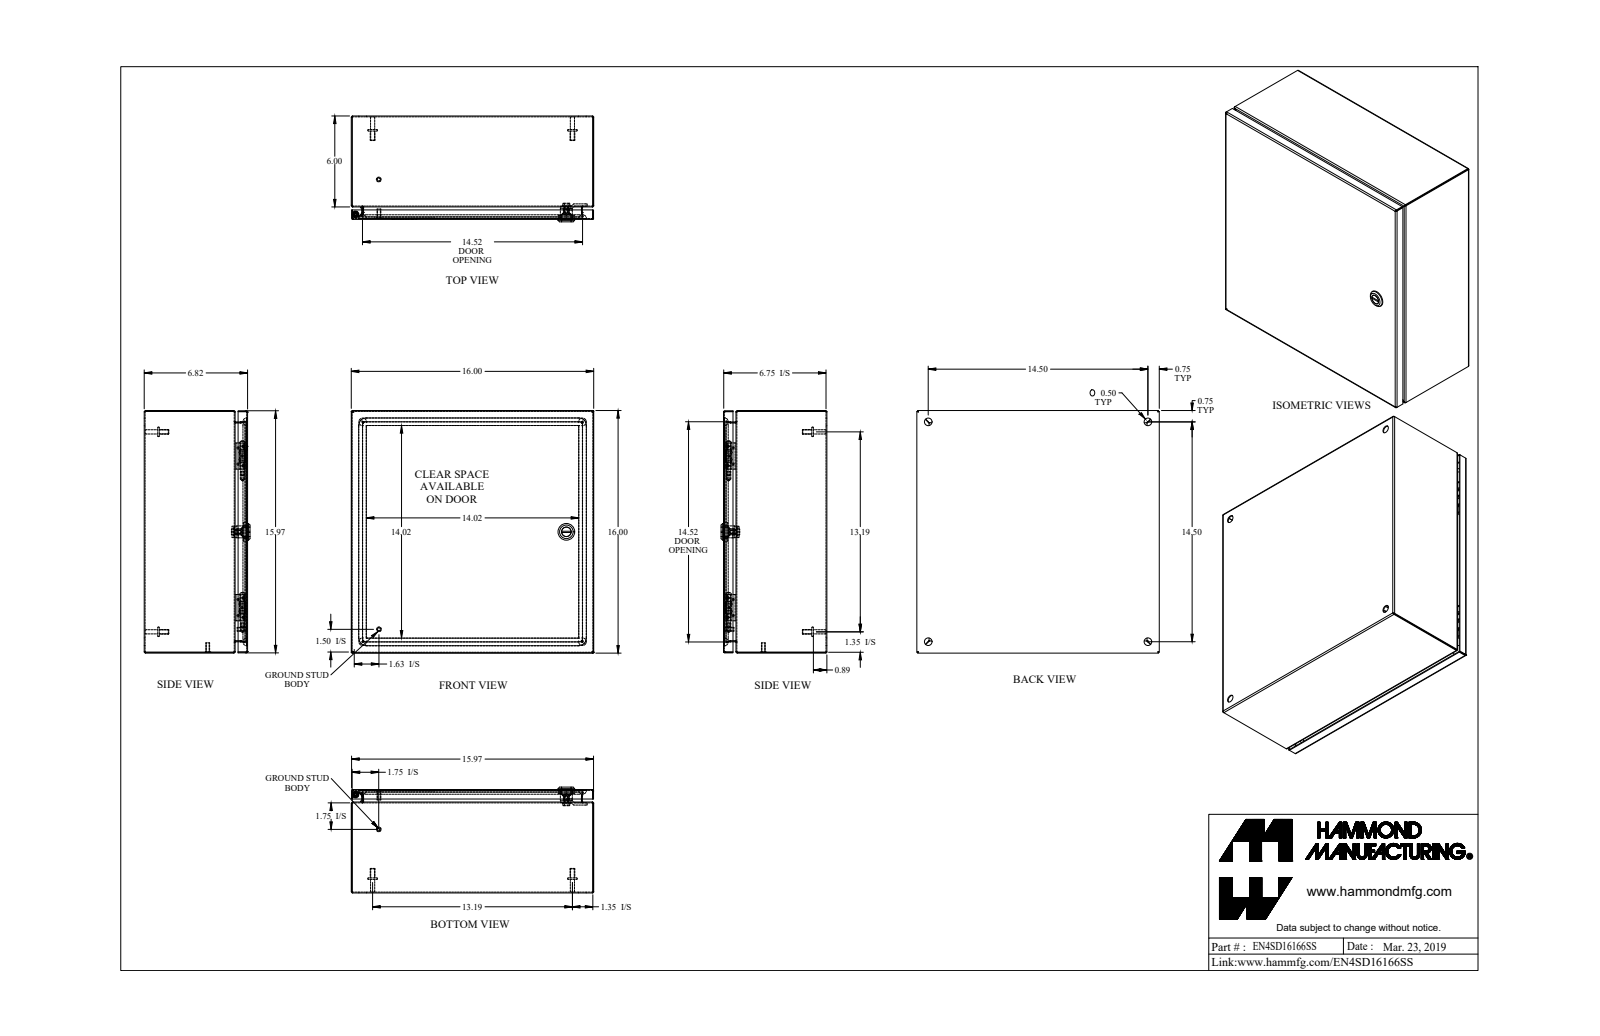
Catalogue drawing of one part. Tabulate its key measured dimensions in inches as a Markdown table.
| quantity | value |
| --- | --- |
| part name | EN4SD16166SS_Default |
| STEP written by | SolidWorks 2019 (CONFIG_CONTROL_DESIGN) |
| units | inches |
| bodies | 22 solids, 657 faces (303 planar, 212 cylindrical, 142 other) |
| overall size | 16 × 16 × 6.982 |
| volume | 64.67 in³ |
| surface area | 2 188 in² |
| round holes (diameter × count) | 0.5 × 5, 0.172 × 1, 0.197 × 1, 0.24 × 1, 0.242 × 1, 0.387 × 1, 0.63 × 1, 0.768 × 1 |
| round bosses / shafts (diameter × count) | 0.313 × 6, 0.625 × 4, 0.275 × 4, 0.25 × 2, 1.1 × 1, 0.785 × 1, 0.625 × 1, 0.525 × 1 |
| partial cylindrical surfaces (radius × count) | 0.029 × 21, 0.086 × 21, 0.188 × 12, 0.006 × 4, 0.062 × 4, 0.25 × 4, 0.499 × 4, 0.125 × 2 |
| main face-to-face distances | 0.057, 6.765, 15.943, 6.708, 6.822, 15.886, 16, 0.822, 5.943, 0.749 |
| hole center spacings | 14.5, 7.327, 15.272, 20.506 |
